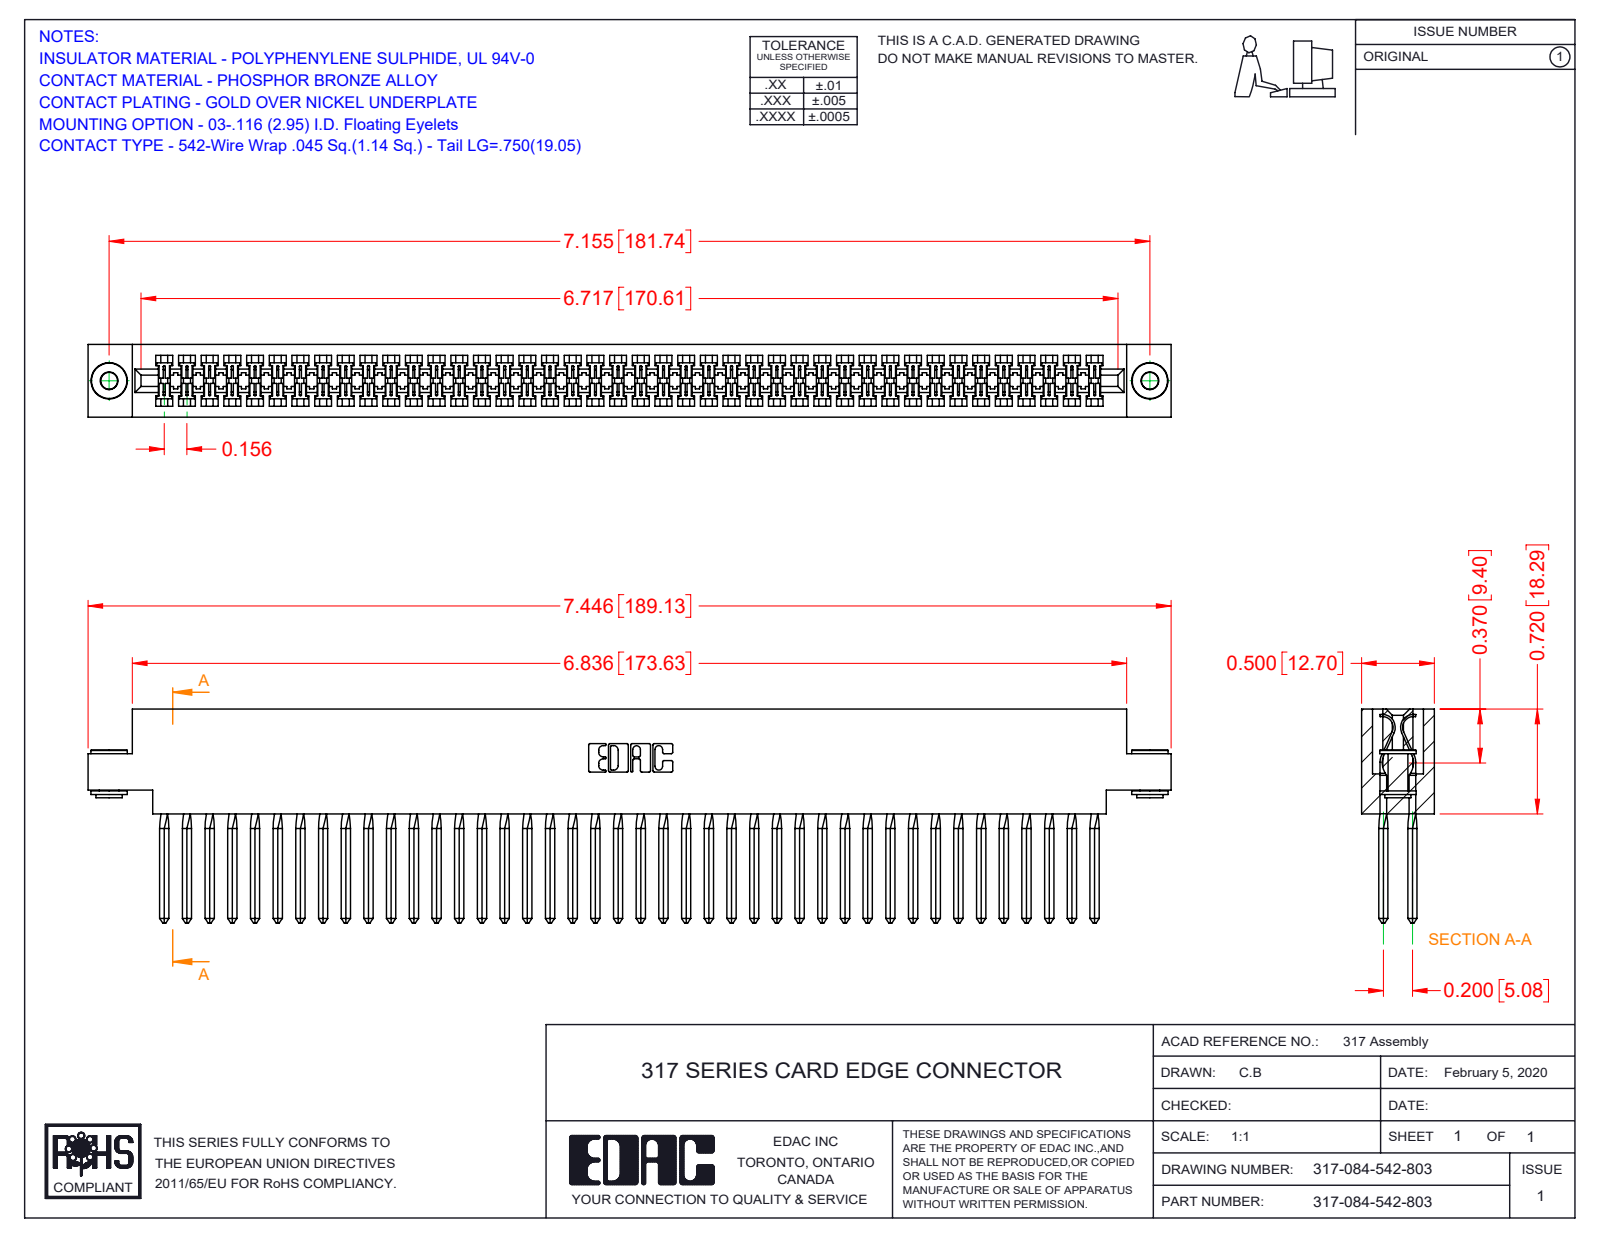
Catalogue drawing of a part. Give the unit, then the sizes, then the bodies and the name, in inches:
Units: inches
Overall size (bounding box): 7.446 × 1.47 × 0.5
Round holes (diameter × count): ⌀0.116 ×2, ⌀0.156 ×2
Round bosses / shafts (diameter × count): ⌀0.25 ×2, ⌀0.18 ×2, ⌀0.136 ×2
Partial cylindrical surfaces — rounded edges, fillets, slot ends (radius × count): R0.006 ×168, R0.01 ×22, R0.007 ×6, R0.031 ×6, R0.026 ×3, R0.074 ×2, R0.089 ×2, R0.1 ×2
Main face-to-face distances: 0.5, 0.075, 0.425, 0.35, 0.2, 0.046, 0.128, 0.372, 0.052, 0.297
Hole centre spacings: 7.155
Volume: 1.891 in³ · Surface area: 67.13 in²
Bodies: 87 solids, 4928 faces (3932 planar, 652 cylindrical, 344 other)
Part name (STEP PRODUCT): 317-084-542-803; 317 Part_.156 Dia - TH; 317-290-003_542; 345-250-002_345-250-002-102
STEP written by: SolidWorks 2016 (CONFIG_CONTROL_DESIGN)
